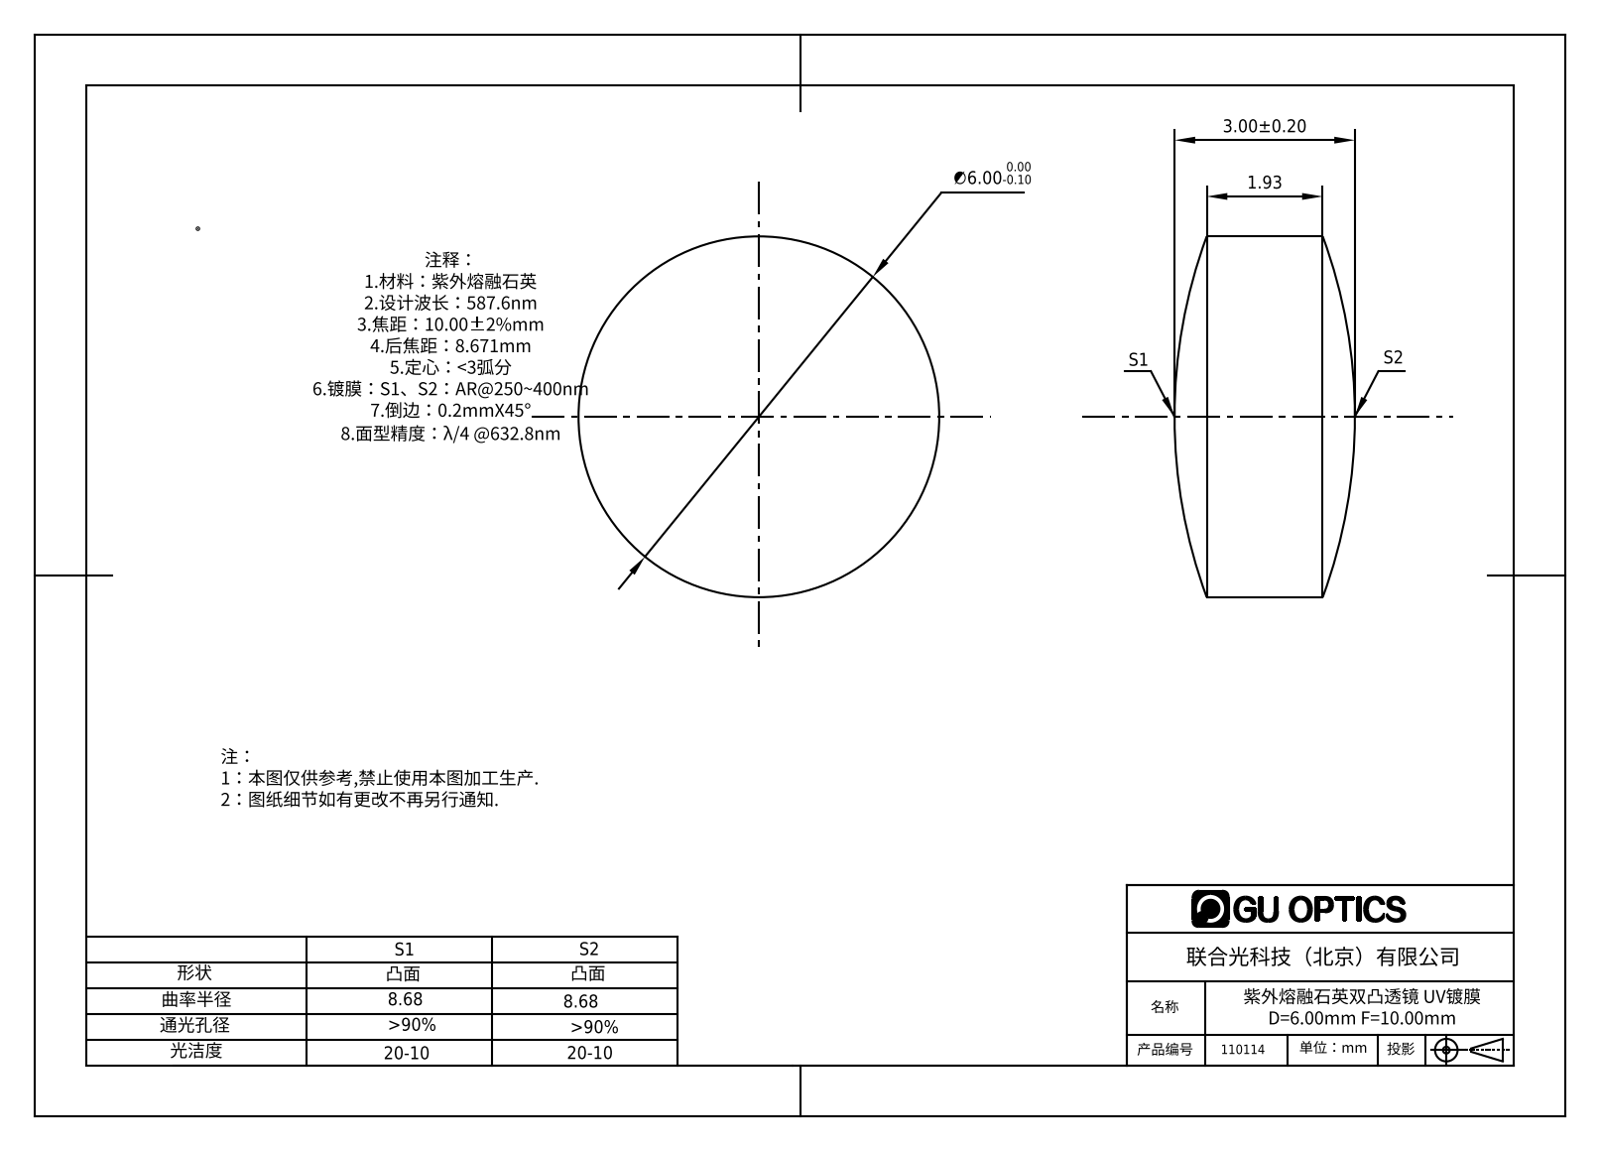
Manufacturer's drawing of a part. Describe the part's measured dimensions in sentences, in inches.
The part is named "110090". Its 3-D file was written by "SolidWorks 2016 (CONFIG_CONTROL_DESIGN)". It is 1 solid with 6 faces: 0 planar, 2 cylindrical and 4 other. Overall it measures 0.236 by 0.236 by 0.118 inches. Its volume is 0.004 cubic inches and its surface area 0.15 square inches. Round bosses or shafts: 1 of diameter 0.236.
